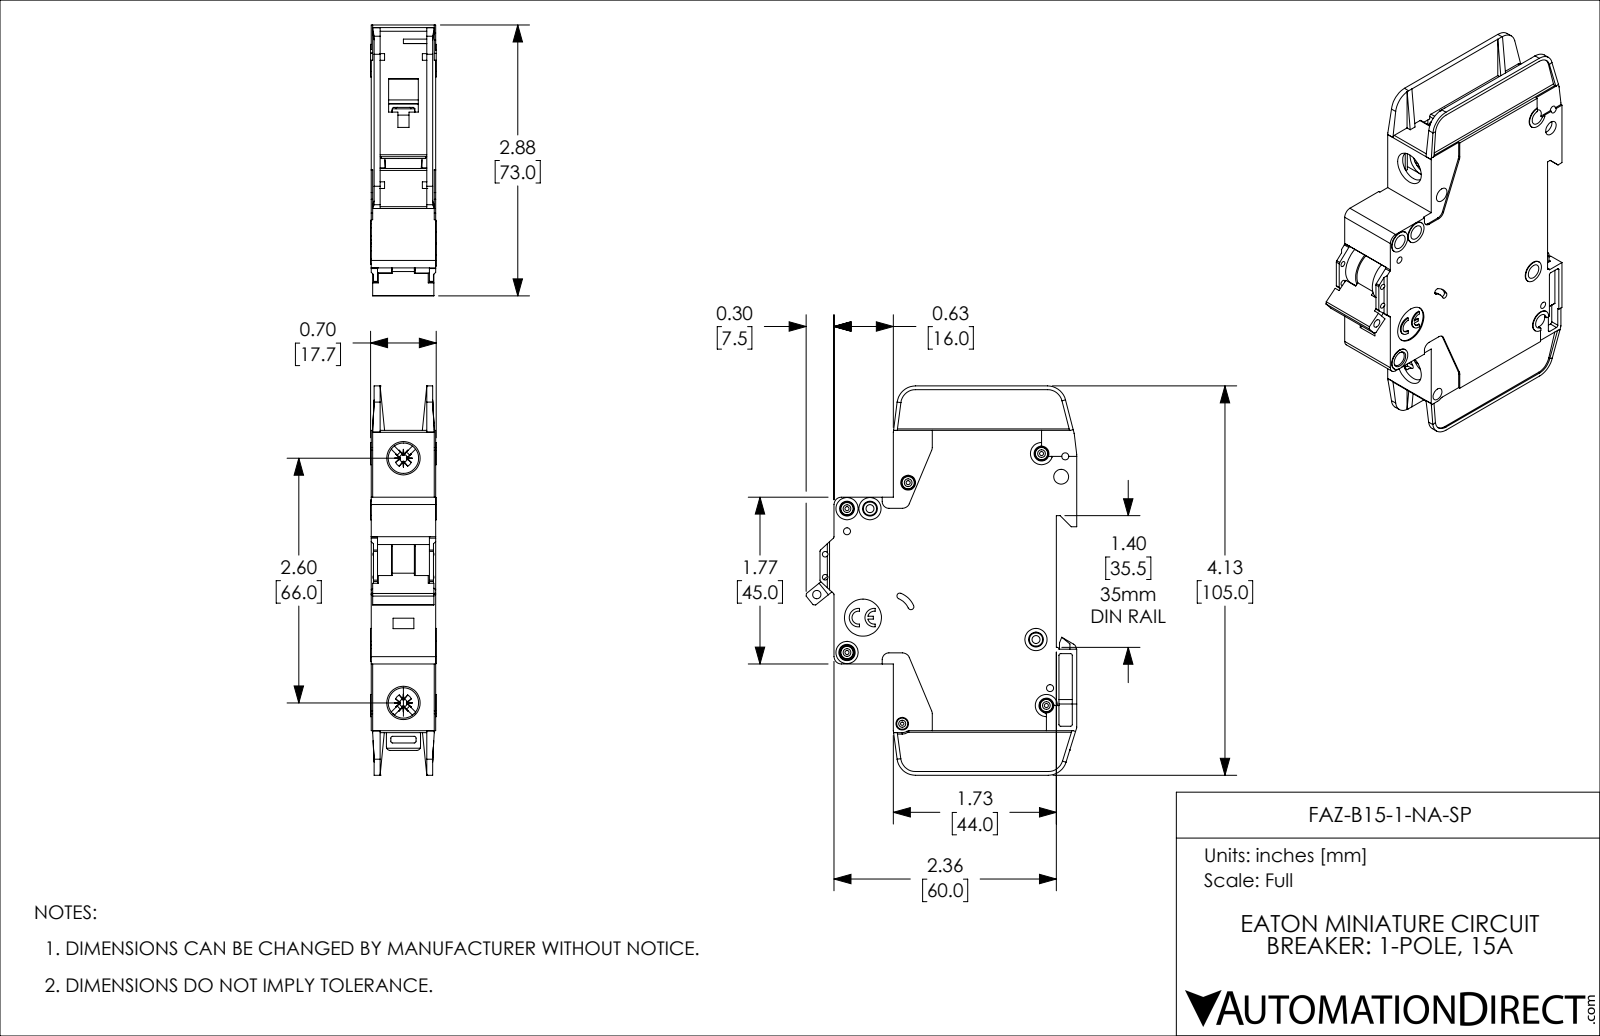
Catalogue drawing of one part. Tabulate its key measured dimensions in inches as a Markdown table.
| quantity | value |
| --- | --- |
| part name | FAZ-B15-1-NA-SP |
| STEP written by | SolidWorks 2019 (AUTOMOTIVE_DESIGN) |
| units | inches |
| bodies | 1 solid, 1127 faces (671 planar, 357 cylindrical, 99 other) |
| overall size | 4.134 × 2.876 × 0.697 |
| volume | 4.682 in³ |
| surface area | 41.01 in² |
| round holes (diameter × count) | 0.157 × 8, 0.043 × 5, 0.075 × 4, 0.059 × 2, 0.085 × 2, 0.323 × 2, 0.035 × 1, 0.089 × 1, 0.098 × 1, 0.134 × 1, 0.394 × 1 |
| round bosses / shafts (diameter × count) | 0.13 × 5, 0.236 × 4, 0.118 × 2, 0.098 × 1 |
| partial cylindrical surfaces (radius × count) | 0.02 × 42, 0.016 × 10, 0.039 × 10, 0.079 × 8, 0.197 × 5, 0.008 × 4, 0.026 × 4, 0.043 × 4 |
| main face-to-face distances | 0.047, 0.685, 0.591, 0.638, 0.094, 0.543, 0.016, 0.031, 0.496, 0.575 |
| hole center spacings | 0.244, 0.537, 0.87, 0.189, 0.199, 0.204, 0.221, 0.24 |
